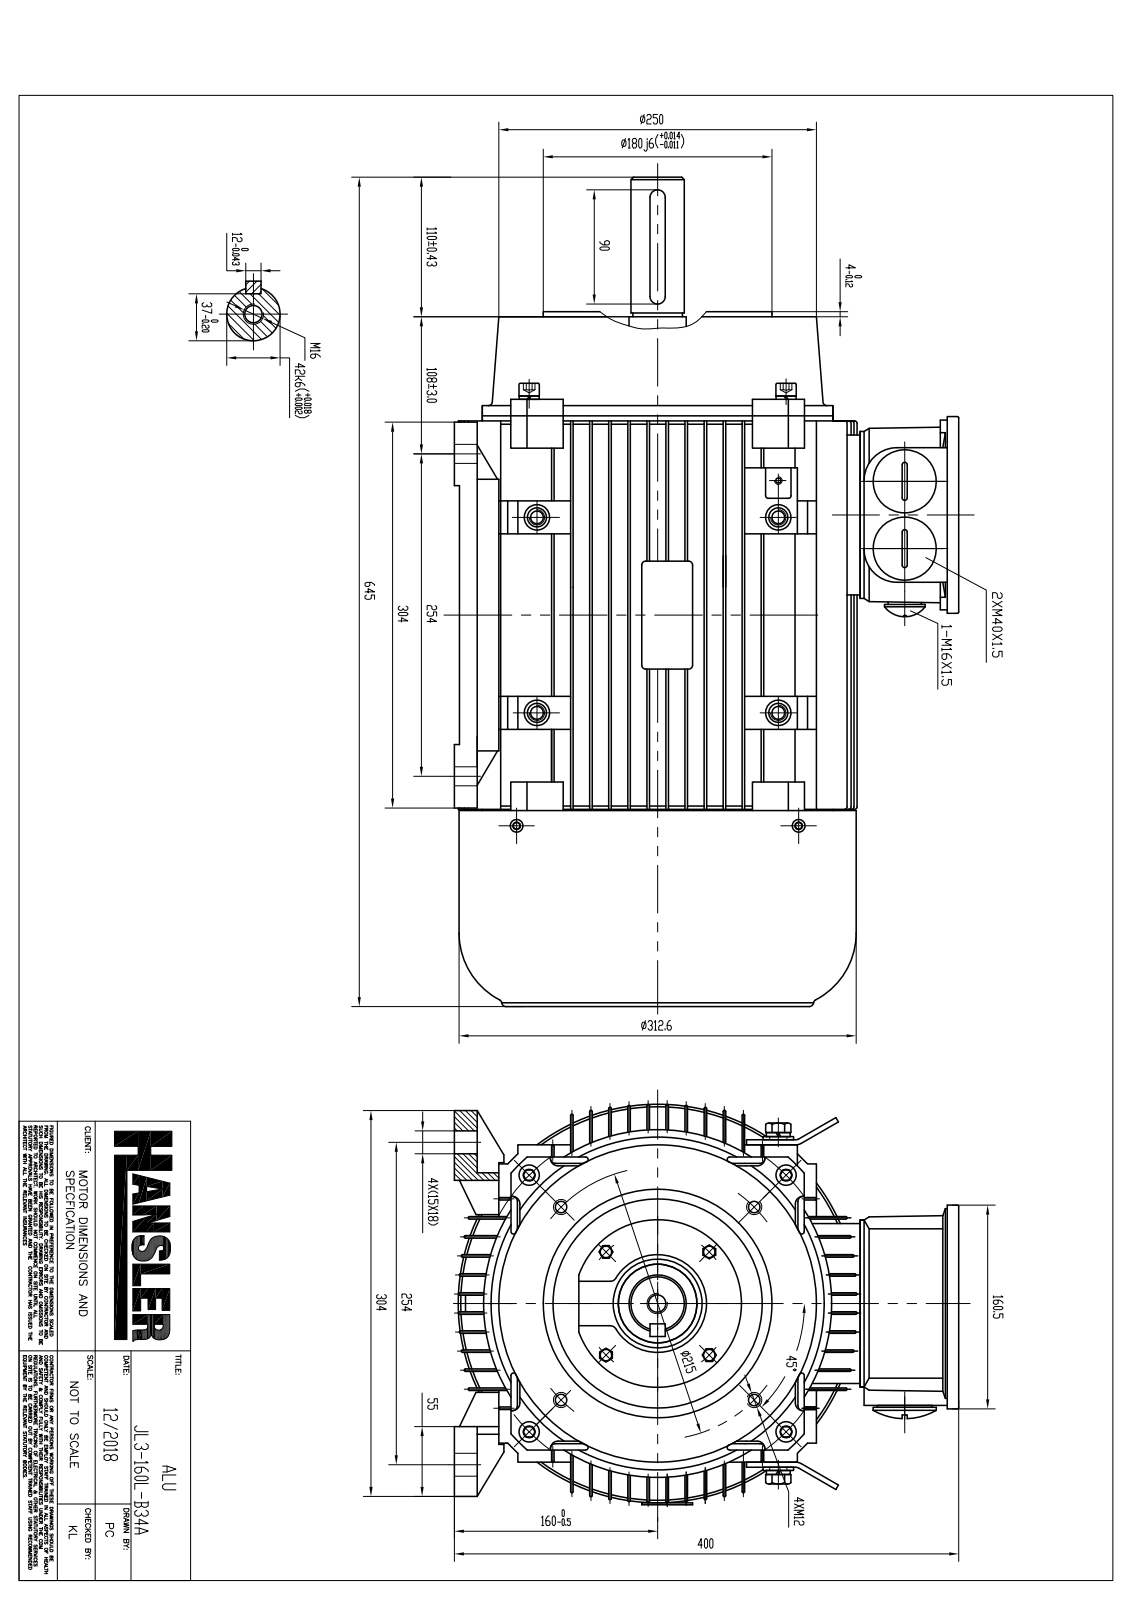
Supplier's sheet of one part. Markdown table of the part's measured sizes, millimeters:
| quantity | value |
| --- | --- |
| part name | JL3-160L-B34A |
| STEP written by | SIEMENS PLM Software NX 10.0 (AUTOMOTIVE_DESIGN) |
| units | millimeters |
| bodies | 71 solids, 8681 faces (3992 planar, 2185 cylindrical, 2504 other) |
| overall size | 633 × 402.7 × 316 |
| volume | 8 105 000 mm³ |
| surface area | 2 790 000 mm² |
| round holes (diameter × count) | 5 × 28, 4.12 × 12, 10 × 12, 8 × 9, 8.39 × 8, 9.1 × 8, 21 × 8, 5.25 × 5, 5.3 × 5, 6 × 5, 16 × 5, 4.2 × 4 |
| round bosses / shafts (diameter × count) | 8 × 10, 5.38 × 9, 15 × 8, 12.59 × 8, 7.19 × 8, 6 × 8, 10 × 5, 7.85 × 5 |
| partial cylindrical surfaces (radius × count) | 1.2 × 262, 1 × 183, 2 × 156, 3 × 66, 4 × 40, 1.37 × 37, 1.5 × 26, 3.42 × 25 |
| main face-to-face distances | 15, 30, 2, 45, 90, 13, 17, 75, 60, 105 |
| hole center spacings | 202.36, 178.9, 202.24, 154.13, 202.23, 121.91, 202.22, 14.64 |
